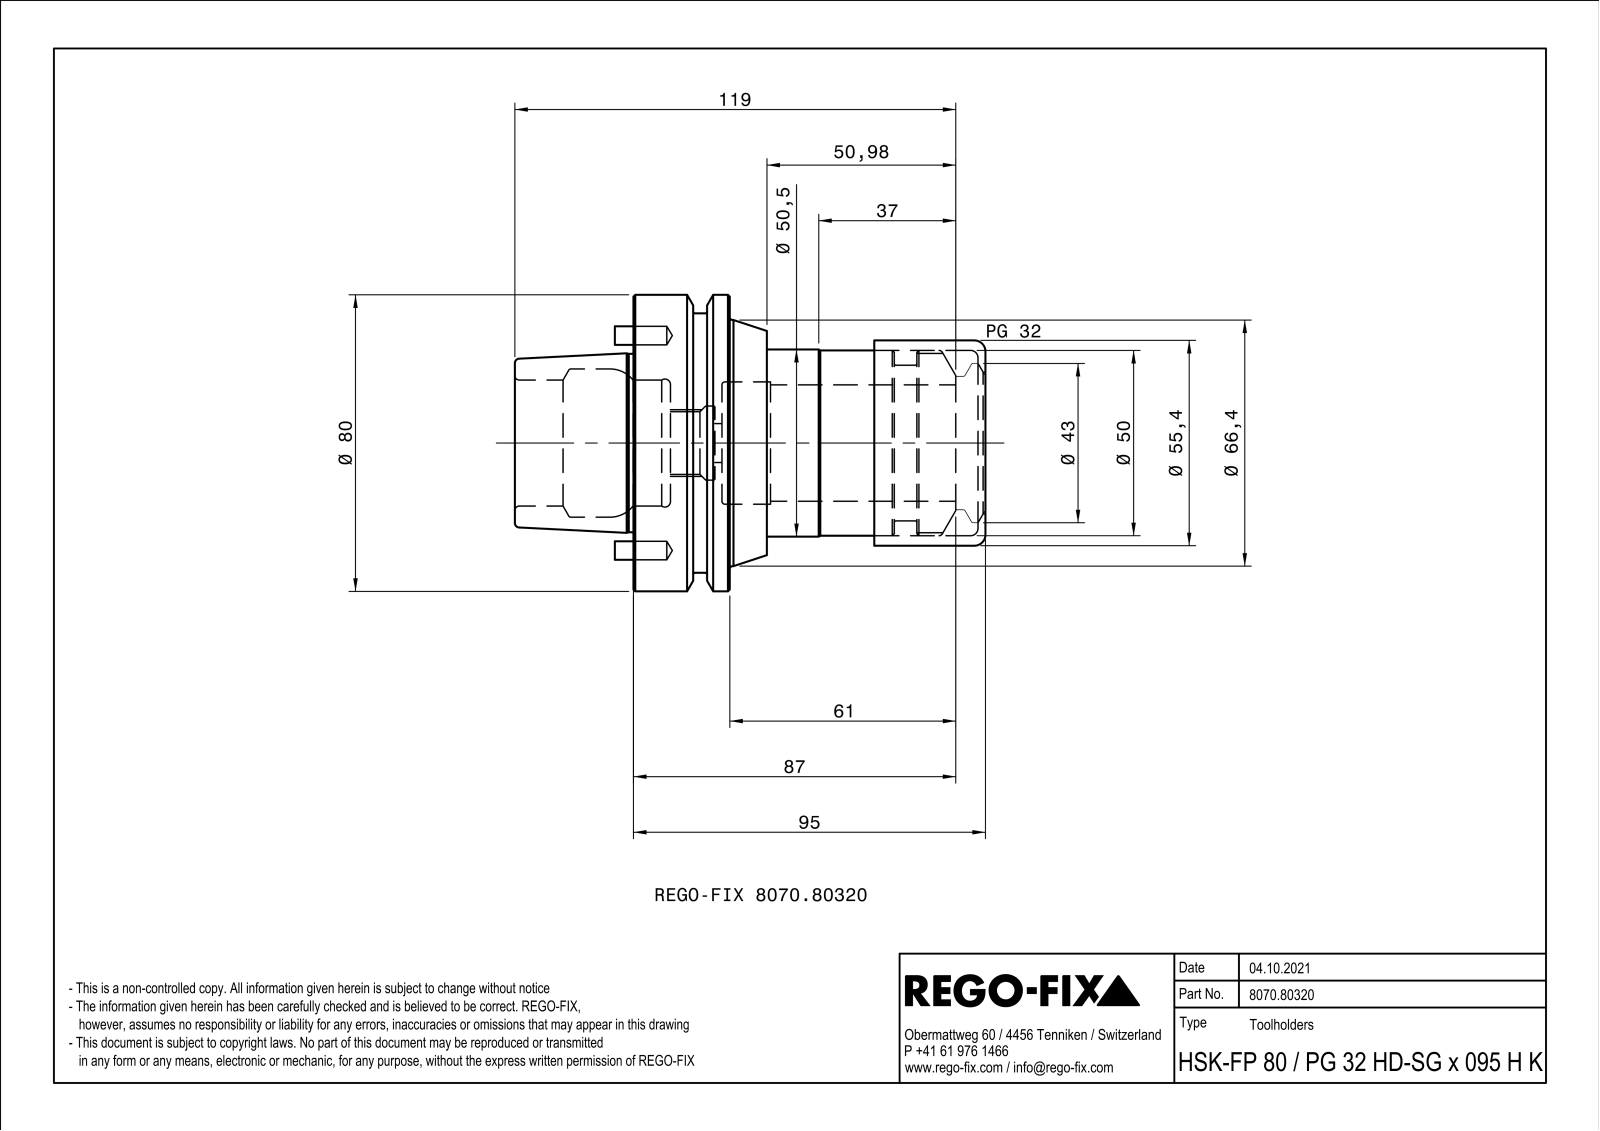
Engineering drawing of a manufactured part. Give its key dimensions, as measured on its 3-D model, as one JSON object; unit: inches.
{"part_name": "0023461", "step_written_by": "SIEMENS PLM Software Solid Edge ST10 (AUTOMOTIVE_DESIGN)", "units": "inches", "bodies": {"solids": 6, "faces": 108, "planar": 32, "cylindrical": 32, "other": 44}, "overall_size": [5, 3.15, 3.15], "volume_in3": 13.69, "surface_area_in2": 89.97, "round_holes": [[0.157, 2], [0.177, 2], [0.197, 2], [0.413, 1], [0.666, 1], [0.787, 1], [1.299, 1], [1.339, 1], [1.506, 1], [1.575, 1], [1.905, 1], [1.97, 1]], "round_bosses_or_shafts": [[0.177, 2], [3.15, 1], [2.756, 1], [2.614, 1], [2.181, 1], [2.165, 1], [1.988, 1], [1.969, 1]], "face_to_face_distances": [1.024, 0.394, 1.417, 2.717, 0.635, 0.783, 0.241, 0.389, 2.323, 3.74], "hole_center_spacings": [1.142, 2.283]}
